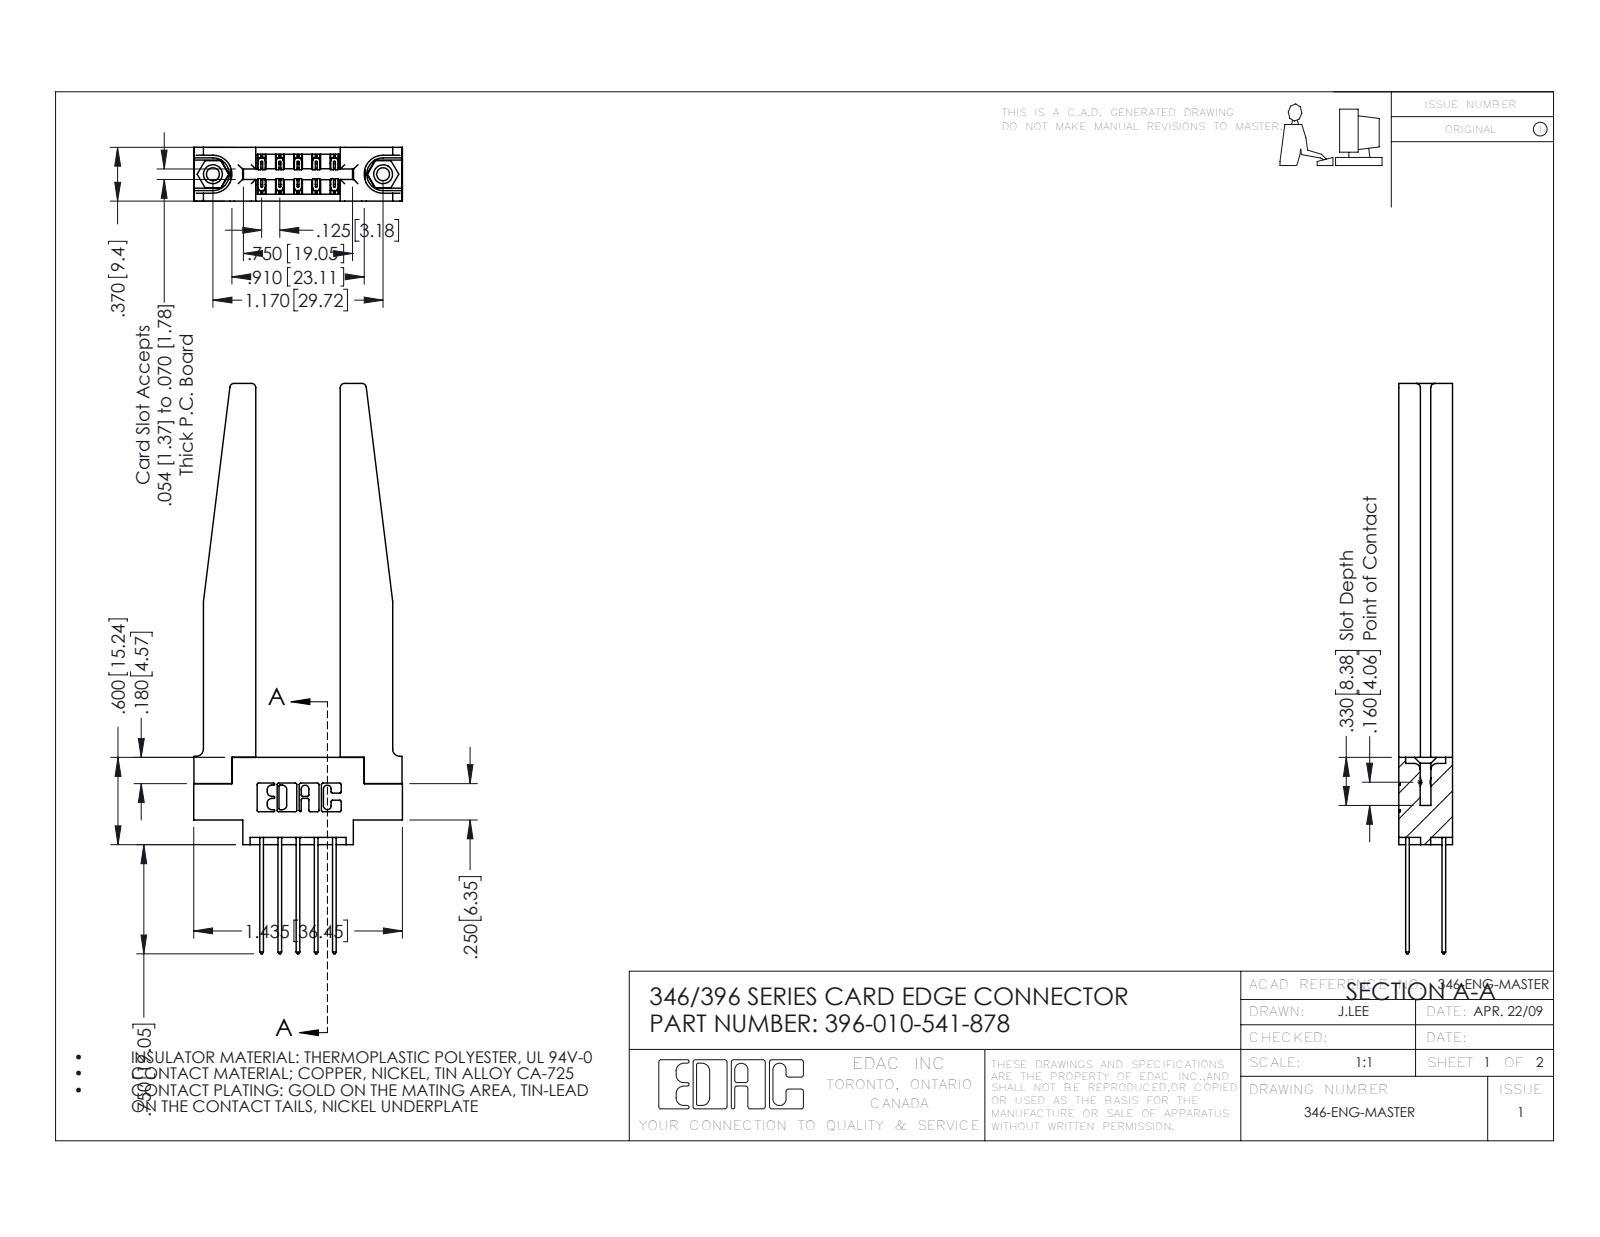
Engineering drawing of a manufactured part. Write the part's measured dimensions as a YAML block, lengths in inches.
part_name: "345-292-001_345-293-141; 396-010-541-878; 346-220-078_345-220-078; 345-250-001_345-250-001-102 (+1 more)"
step_written_by: "SolidWorks 2016 (CONFIG_CONTROL_DESIGN)"
units: inches
bodies: {solids: 15, faces: 880, planar: 572, cylindrical: 256, other: 52}
overall_size: [3.92, 1.435, 0.37]
volume: 0.615
surface_area: 16.69
round_holes:
  - {diameter: 0.089, count: 2}
  - {diameter: 0.125, count: 2}
  - {diameter: 0.156, count: 2}
  - {diameter: 0.064, count: 1}
round_bosses_or_shafts:
  - {diameter: 0.155, count: 2}
partial_cylinders:
  - {radius: 0.01, count: 22}
  - {radius: 0.006, count: 15}
  - {radius: 0.01, count: 10}
  - {radius: 0.03, count: 8}
  - {radius: 0.007, count: 6}
  - {radius: 0.031, count: 6}
  - {radius: 0.026, count: 3}
  - {radius: 0.014, count: 2}
face_to_face_distances: [0.37, 0.15, 0.22, 0.25, 0.072, 0.148, 0.581, 0.102, 0.048, 0.322]
hole_center_spacings: [0.246, 0.969, 1.17]
